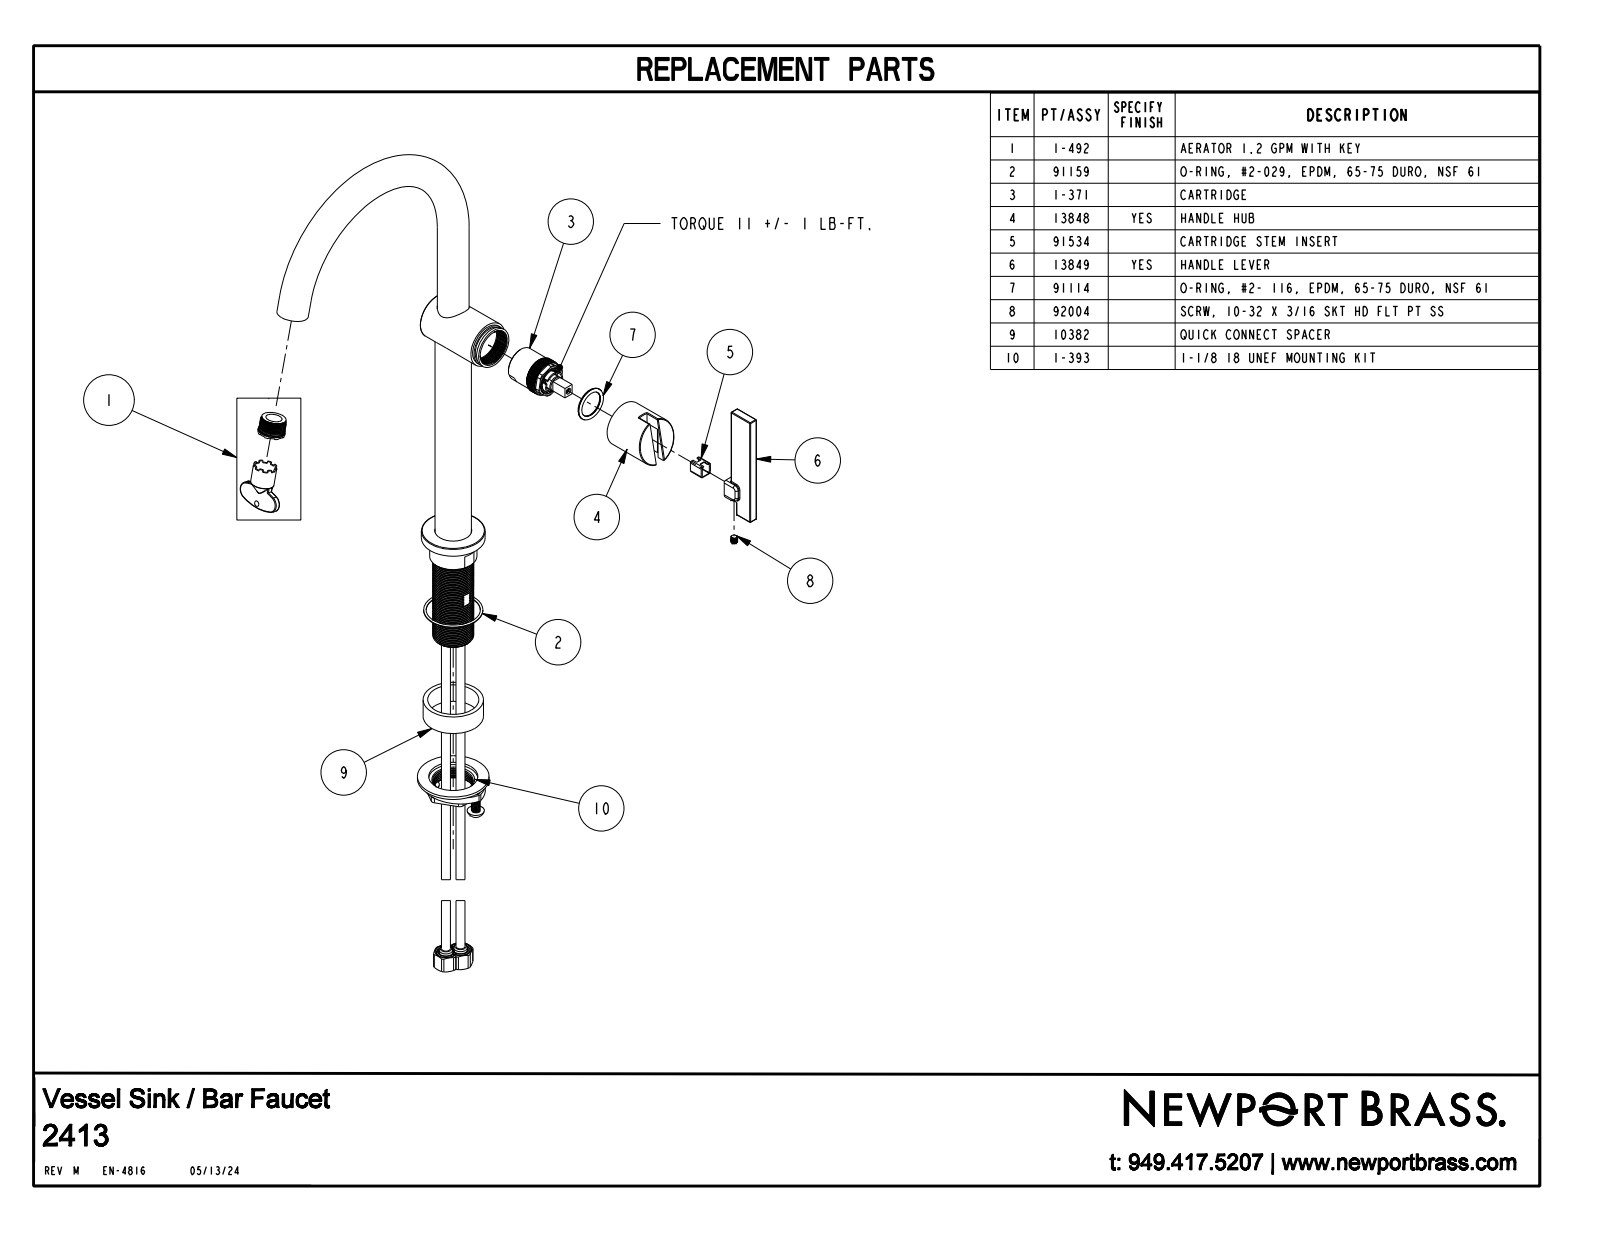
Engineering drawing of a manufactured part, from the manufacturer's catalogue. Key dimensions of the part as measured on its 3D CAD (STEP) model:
Part name (STEP PRODUCT): 2413
STEP written by: CREO PARAMETRIC BY PTC INC, 2018400 (AUTOMOTIVE_DESIGN)
Units: inches
Bodies: 1 solid, 78 faces (18 planar, 32 cylindrical, 28 other)
Overall size (bounding box): 13.994 × 7.551 × 3.84
Volume: 16.28 in³ · Surface area: 77.42 in²
Round bosses / shafts (diameter × count): ⌀0.875 ×2, ⌀1.75 ×1, ⌀1.25 ×1
Partial cylindrical surfaces — rounded edges, fillets, slot ends (radius × count): R0.02 ×20
Main face-to-face distances: 0.25, 0.25, 3.59, 0.747, 2.84, 0.75, 2.604, 0.237, 0.987, 2.44
